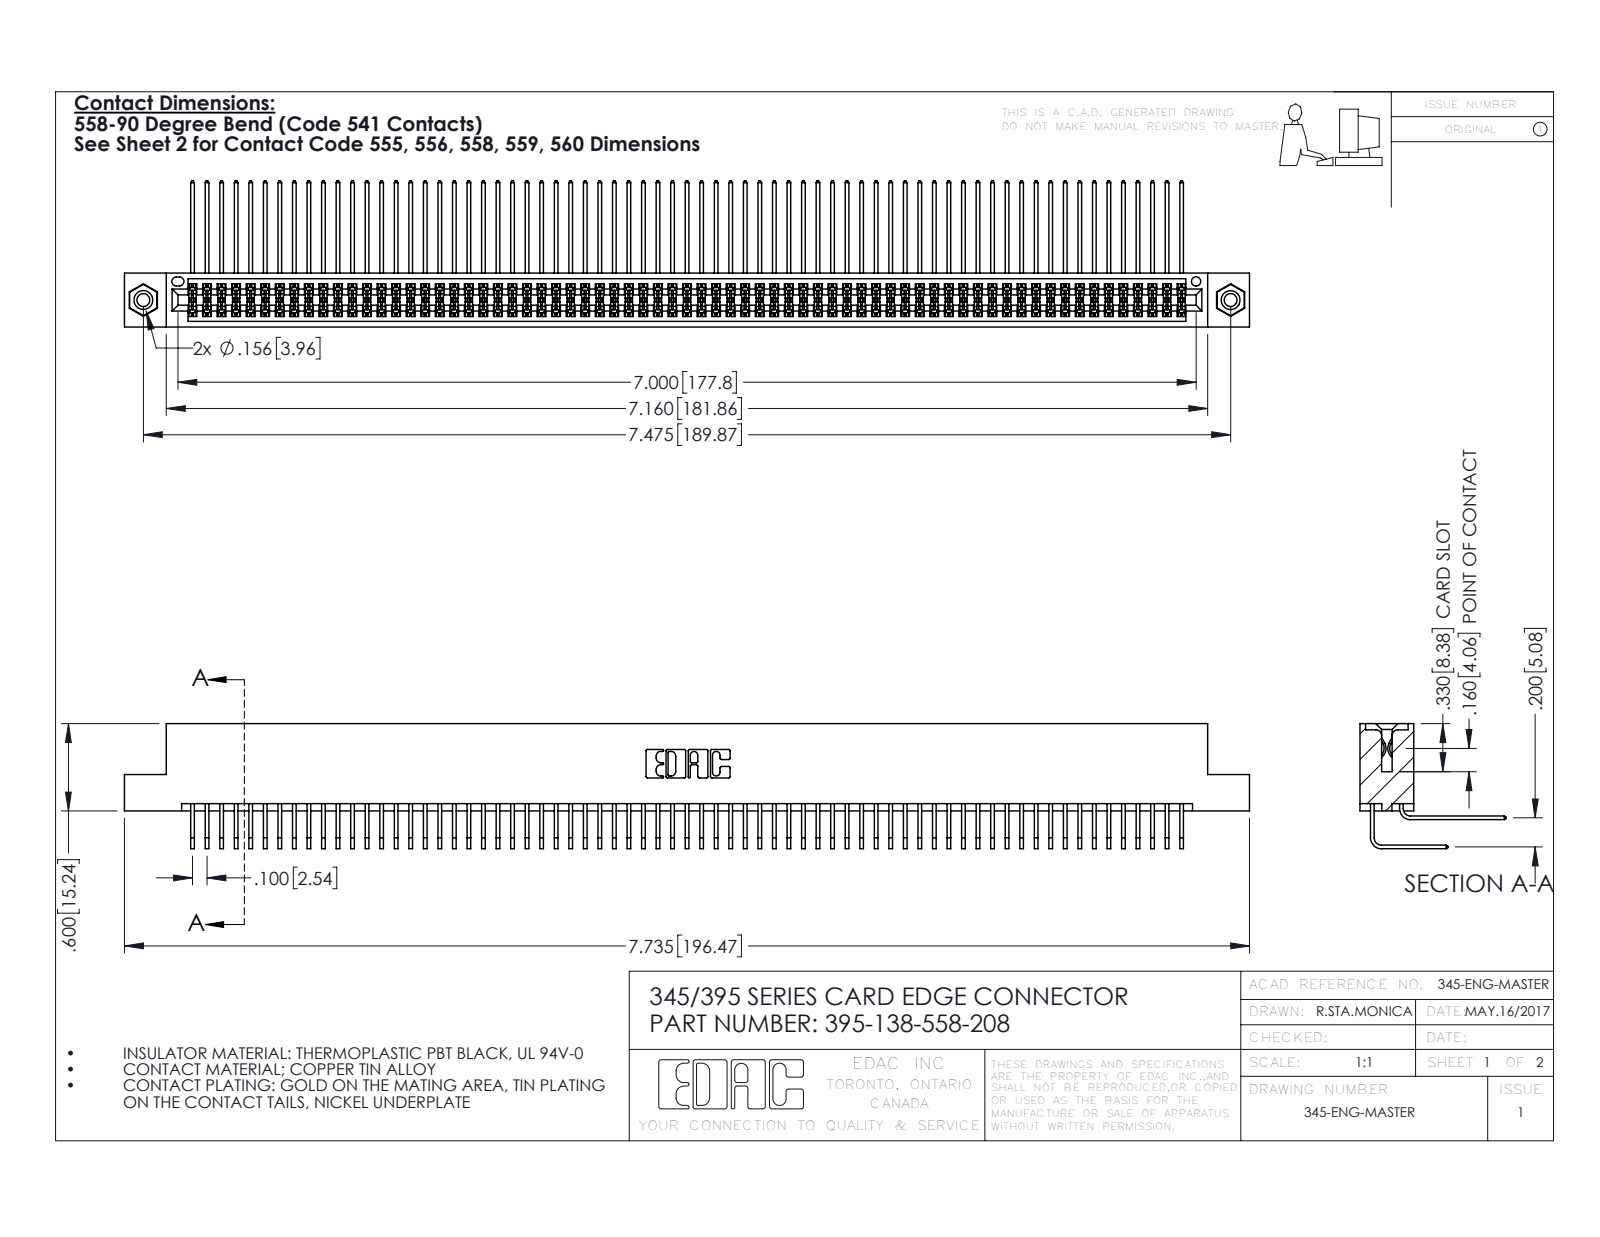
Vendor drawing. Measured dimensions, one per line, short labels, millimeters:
name: 395-138-558-208; 345-292-001_558 559 Tail - 1; 345-292-001_558 Tail - 2; 345 Part_Flush Mounting Lugs - 0.156 Dia-TI (+1 more)
written by: SolidWorks 2016 (CONFIG_CONTROL_DESIGN)
unit: mm
bodies: 141 solids, 7362 faces (4942 planar, 2404 cylindrical, 16 other)
size: 196.5 × 25.5 × 21.8
volume: 20 120 mm³; area: 34 030 mm²
holes: 2× ⌀2.3, 2× ⌀3.2, 2× ⌀4, 1× ⌀1.6
bosses: 2× ⌀3.9
rounds: 275× R0.2, 22× R0.3, 6× R0.2, 6× R0.8, 3× R0.7, 2× R0.4, 2× R0.5, 2× R0.6
face distances: 1.8, 7.6, 5.1, 9.4, 2.5, 6.9, 0.6, 5.7, 0.6, 4.4
hole spacings: 6.9, 183.9, 189.9
